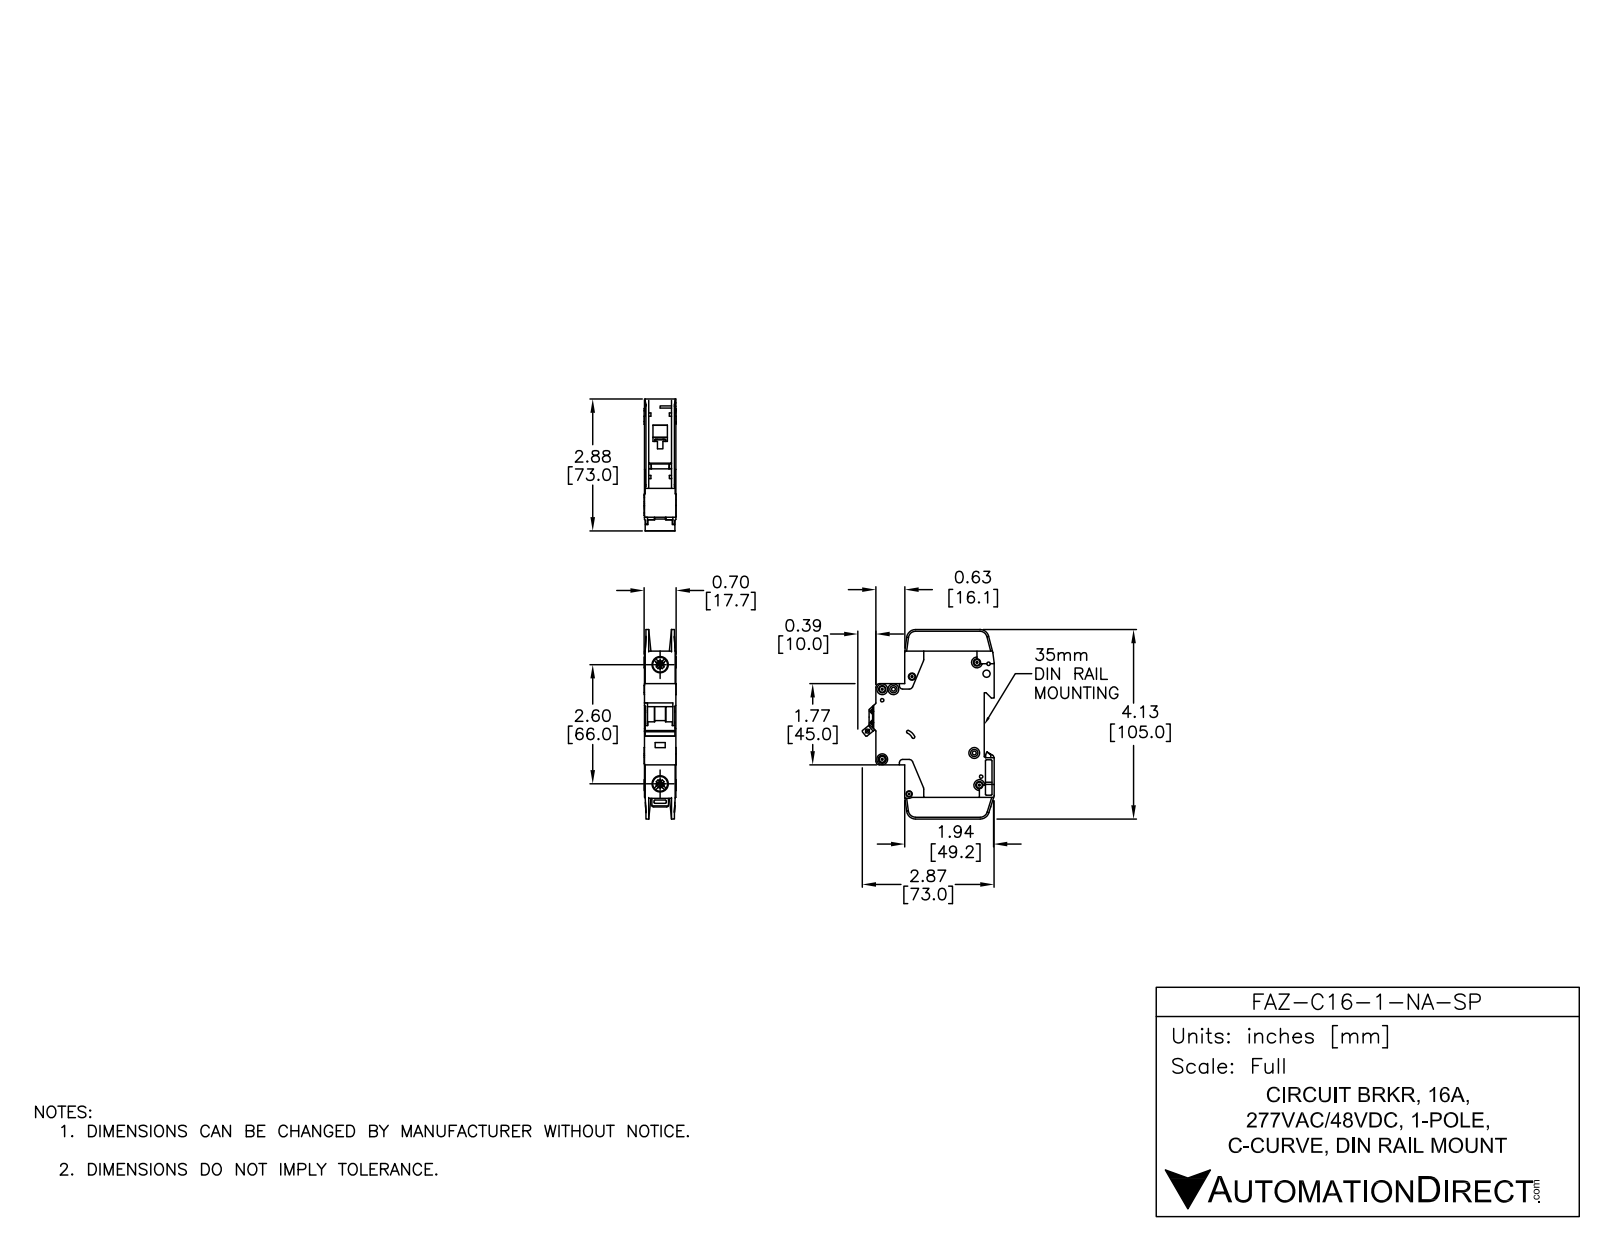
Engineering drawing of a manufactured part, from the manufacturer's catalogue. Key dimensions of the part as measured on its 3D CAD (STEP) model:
Part name (STEP PRODUCT): FAZ-C16-1-NA-SP
STEP written by: SolidWorks 2014 (AUTOMOTIVE_DESIGN)
Units: millimetres
Bodies: 3 solids, 784 faces (409 planar, 263 cylindrical, 112 other)
Overall size (bounding box): 105 × 73.04 × 17.7
Volume: 77 695 mm³ · Surface area: 24 740 mm²
Round holes (diameter × count): ⌀3.6 ×7, ⌀1.09 ×2, ⌀1.5 ×2, ⌀4 ×2, ⌀7.15 ×2, ⌀8.2 ×2, ⌀1.9 ×1, ⌀2.15 ×1, ⌀2.2 ×1, ⌀2.55 ×1, ⌀3.3 ×1, ⌀3.4 ×1
Round bosses / shafts (diameter × count): ⌀6 ×7, ⌀2.5 ×1
Partial cylindrical surfaces — rounded edges, fillets, slot ends (radius × count): R0.25 ×29, R0.5 ×18, R1 ×10, R2 ×10, R5 ×5, R4 ×4, R1.8 ×3, R0.2 ×2
Main face-to-face distances: 17.5, 15.05, 0.7, 2.45, 1.75, 15.75, 13.3, 14, 12.6, 2
Hole centre spacings: 6.2, 5.19, 6.1, 8.19, 8.56, 8.7, 11.11, 12.45
